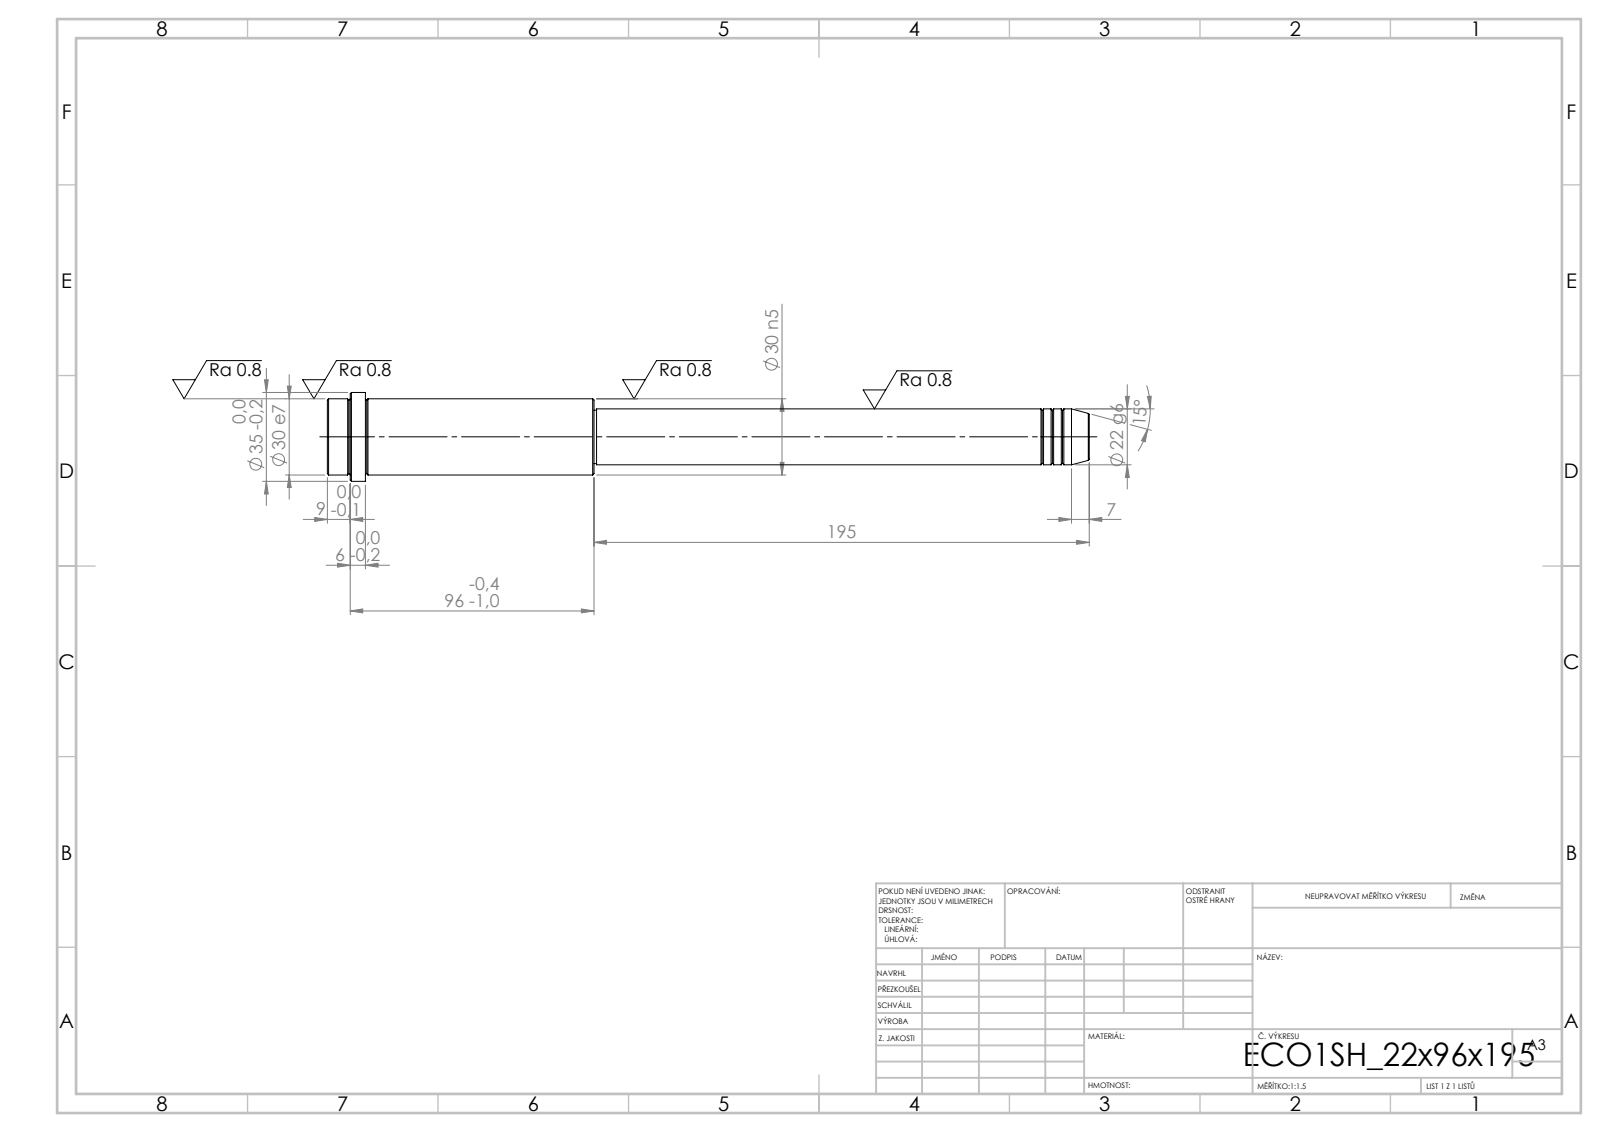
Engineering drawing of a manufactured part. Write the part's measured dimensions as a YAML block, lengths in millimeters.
step_written_by: "SolidWorks 2019 (CONFIG_CONTROL_DESIGN)"
units: millimeters
bodies: {solids: 1, faces: 52, planar: 6, cylindrical: 16, other: 30}
overall_size: [300, 35, 35]
volume: 149224
surface_area: 25427
round_bosses_or_shafts:
  - {diameter: 35, count: 1}
  - {diameter: 30, count: 1}
  - {diameter: 22, count: 1}
  - {diameter: 21, count: 1}
face_to_face_distances: [105, 90, 15, 195, 285, 300, 291, 96, 6, 9]
